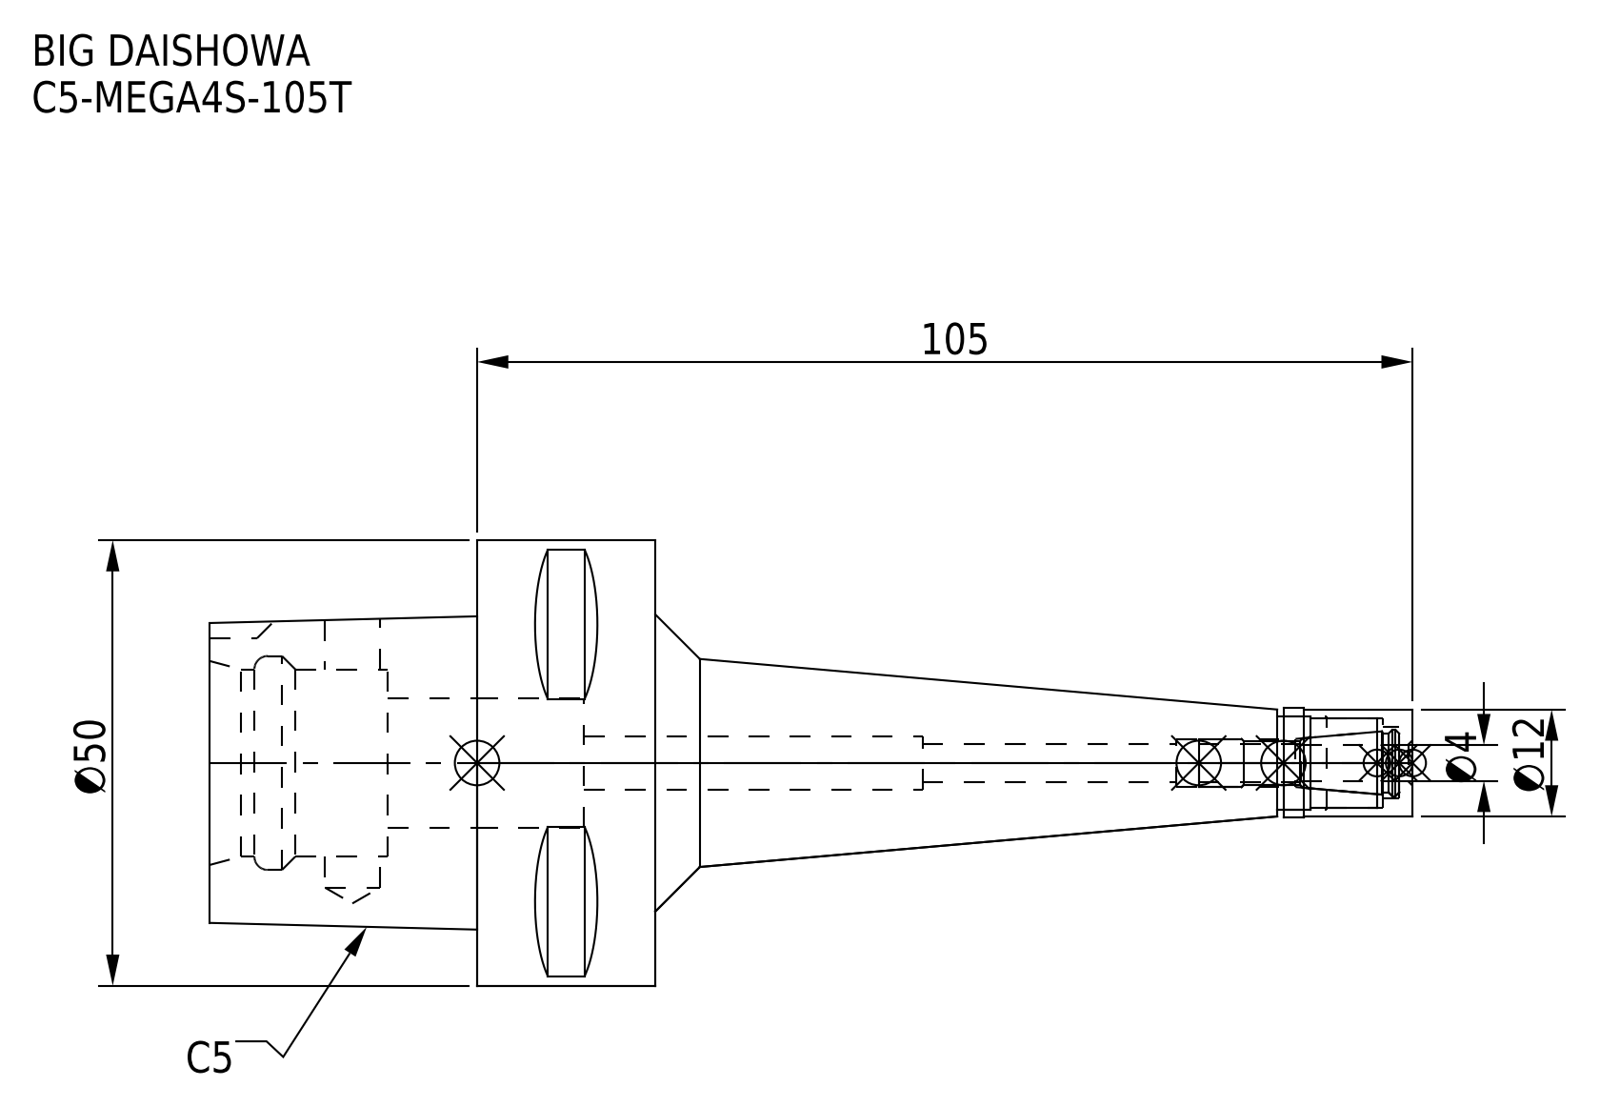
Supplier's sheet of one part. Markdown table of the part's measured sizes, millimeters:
| quantity | value |
| --- | --- |
| part name | C5-MEGA4S-105T; C5-MEGA4S-105T-040.stp; MGN4S_1.stp; C5-MEGA4S-105T-040-FreeParts (+3 more) |
| STEP written by | SolidWorks 2019 (CONFIG_CONTROL_DESIGN) |
| units | millimeters |
| bodies | 2 solids, 93 faces (38 planar, 37 cylindrical, 18 other) |
| overall size | 135 × 50 × 50 |
| volume | 73 594 mm³ |
| surface area | 19 445 mm² |
| round holes (diameter × count) | 4.1 × 1, 4.2 × 1, 5.4 × 1, 6 × 1, 6.1 × 1, 8 × 1, 10 × 1, 10.5 × 1, 14.5 × 1, 21 × 1, 24 × 1 |
| round bosses / shafts (diameter × count) | 50 × 1, 12.3 × 1, 12 × 1 |
| partial cylindrical surfaces (radius × count) | 4 × 1 |
| main face-to-face distances | 20, 30, 50, 44, 10, 19.18, 12, 8, 22, 42 |
